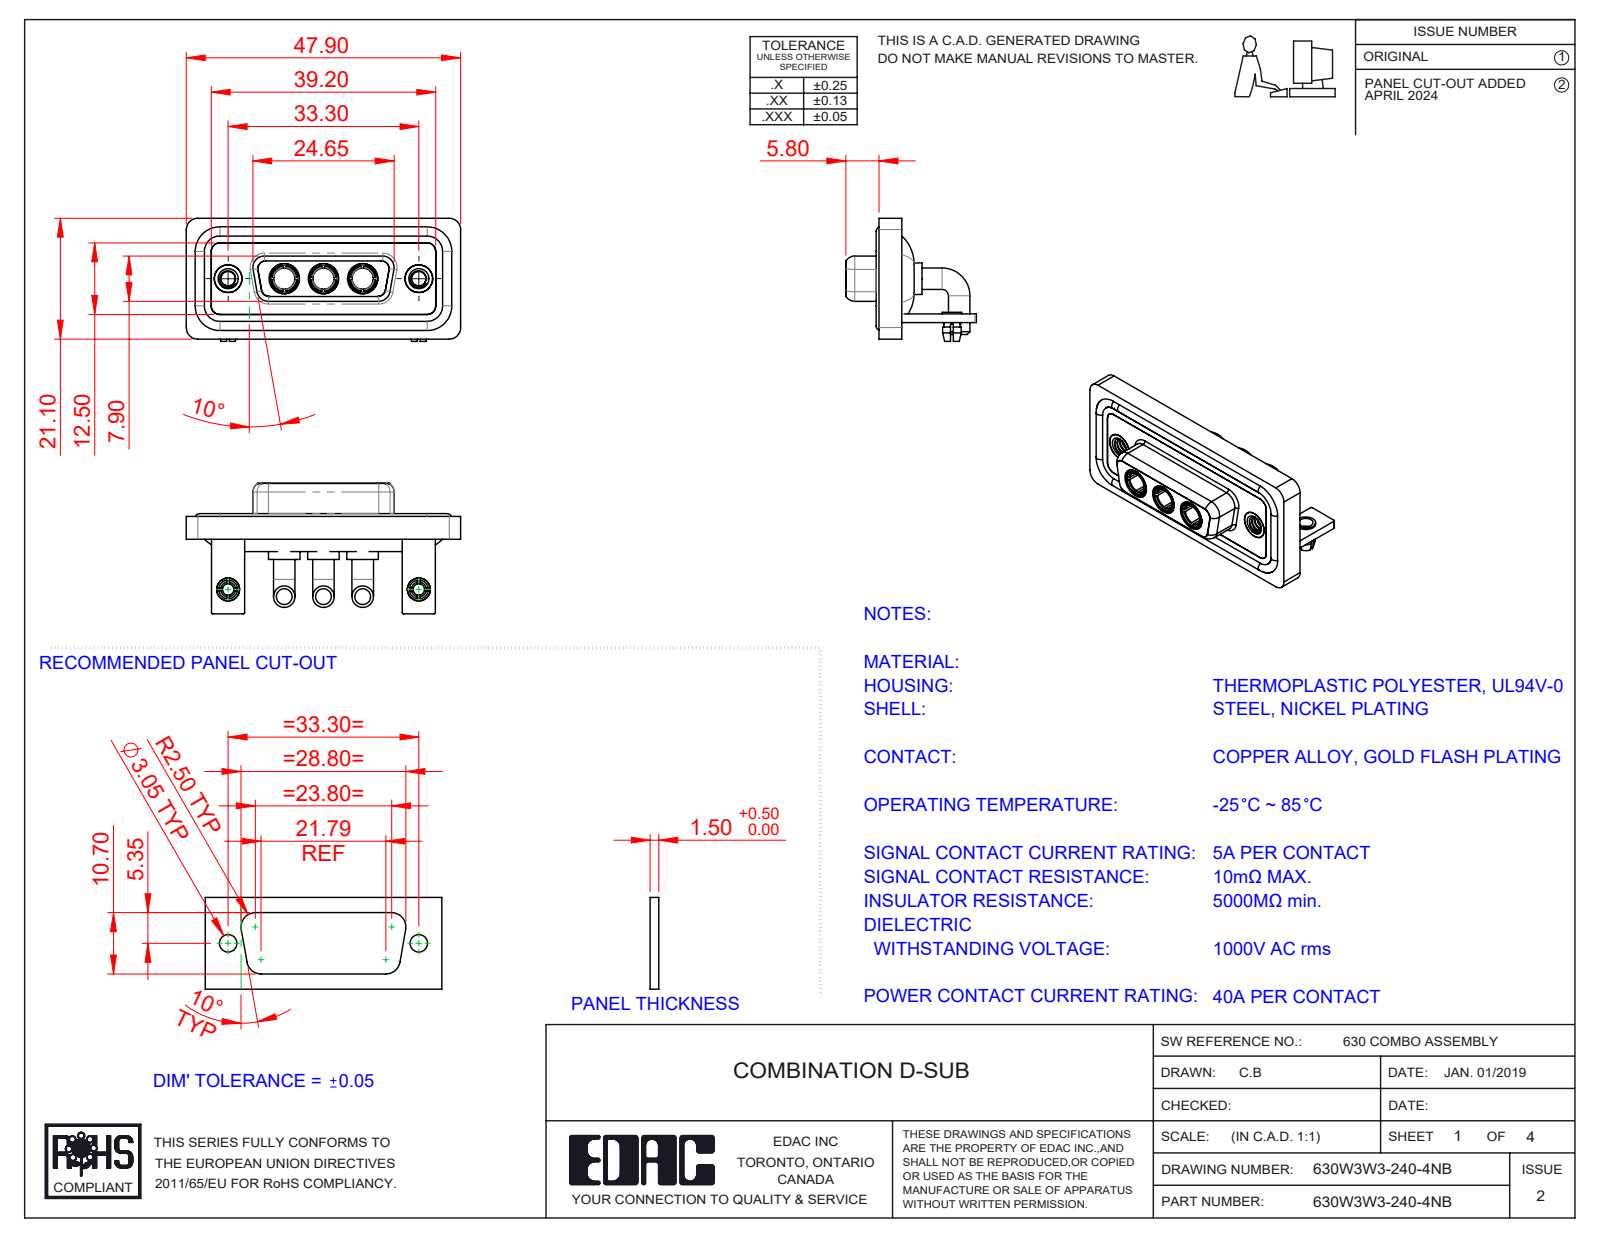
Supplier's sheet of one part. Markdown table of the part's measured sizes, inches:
| quantity | value |
| --- | --- |
| part name | 630Combo Housing_3W3; 630Combo Shell Rear_15 Contacts; 630Combo Threaded Rivet_A; 630Combo Board Lock_50 Contacts (+5 more) |
| STEP written by | SolidWorks 2023 (CONFIG_CONTROL_DESIGN) |
| units | inches |
| bodies | 17 solids, 754 faces (260 planar, 317 cylindrical, 177 other) |
| overall size | 1.886 × 0.898 × 0.846 |
| volume | 0.415 in³ |
| surface area | 17.13 in² |
| round holes (diameter × count) | 0.191 × 5, 0.098 × 4, 0.146 × 3, 0.209 × 3, 0.079 × 2, 0.126 × 2, 0.157 × 2, 0.159 × 2, 0.197 × 2 |
| round bosses / shafts (diameter × count) | 0.148 × 6, 0.063 × 4, 0.217 × 3, 0.205 × 3, 0.195 × 3, 0.187 × 3, 0.195 × 2, 0.189 × 2 |
| partial cylindrical surfaces (radius × count) | 0.079 × 21, 0.059 × 18, 0.01 × 16, 0.053 × 12, 0.063 × 8, 0.02 × 5, 0.024 × 4, 0.026 × 4 |
| main face-to-face distances | 0.016, 0.114, 0.059, 0.071, 0.146, 0.043, 0.161, 0.063, 0.098, 0.055 |
| hole center spacings | 0.27, 0.386, 0.656, 0.925, 1.311, 0.539 |
